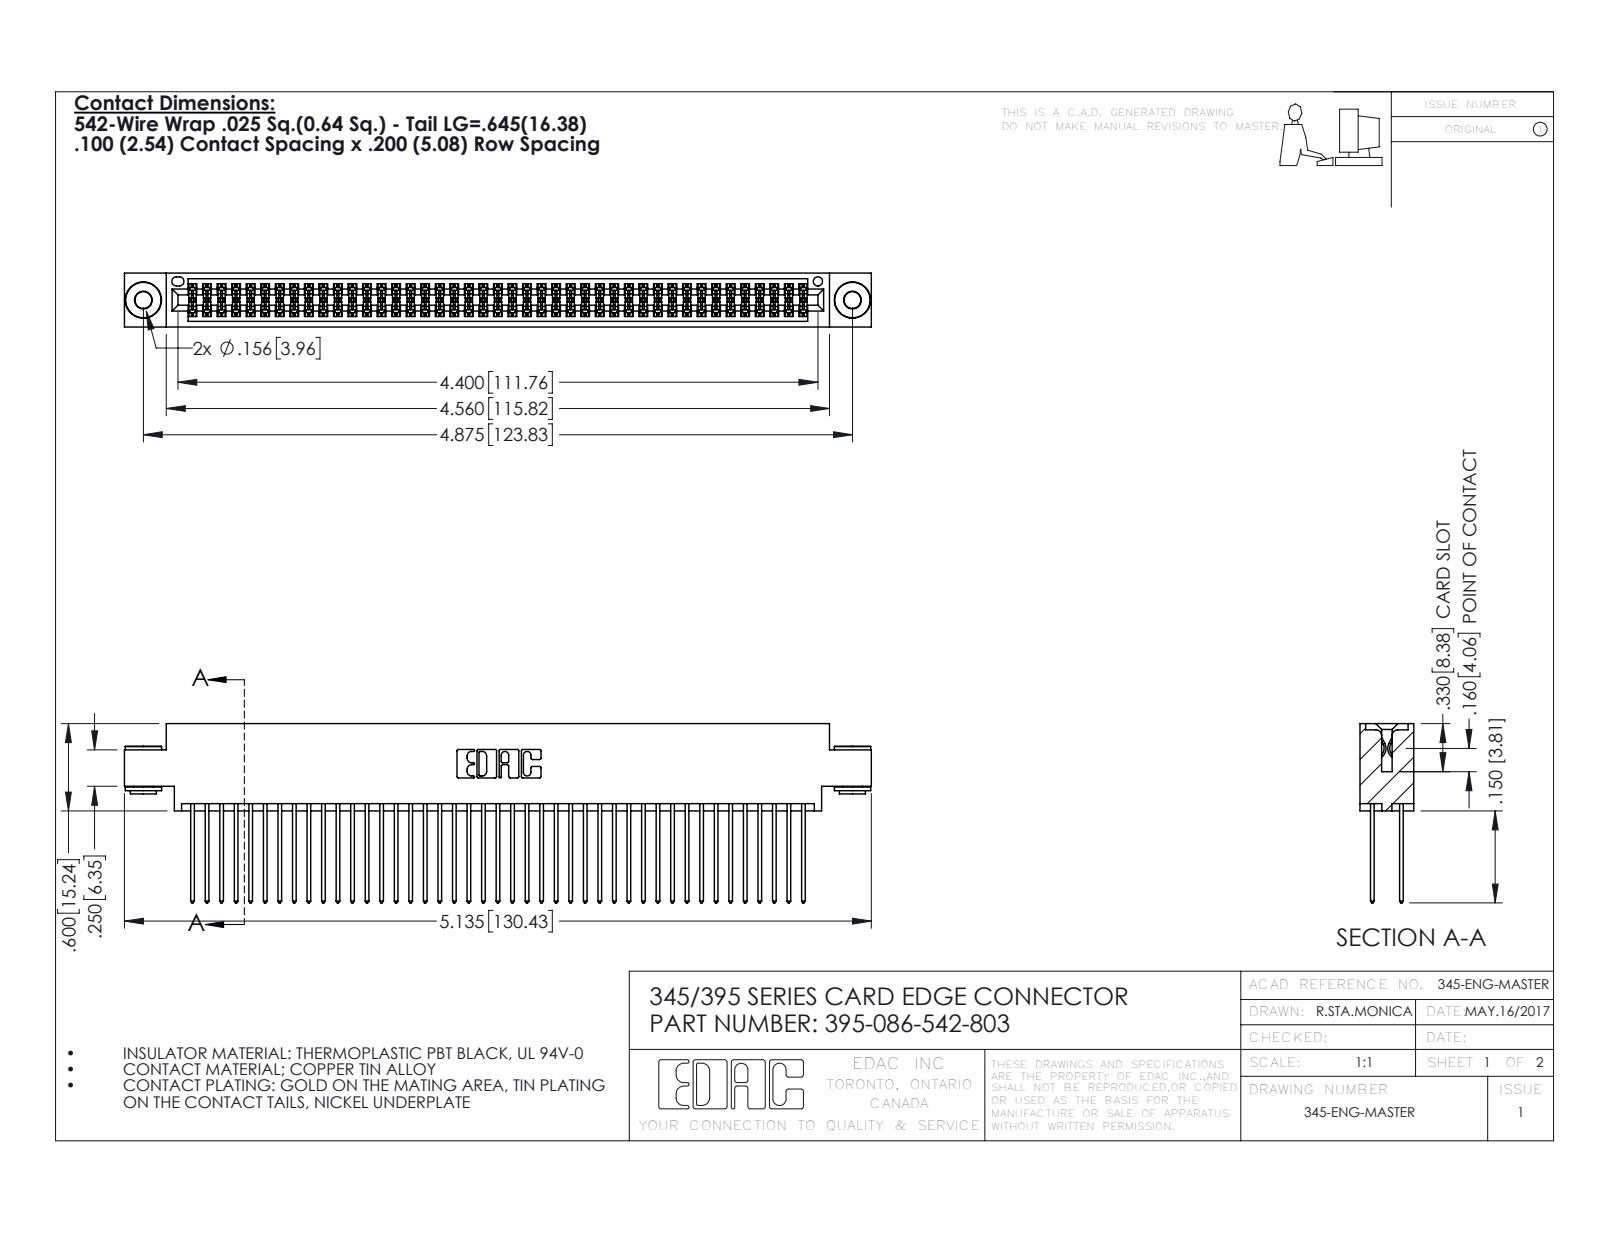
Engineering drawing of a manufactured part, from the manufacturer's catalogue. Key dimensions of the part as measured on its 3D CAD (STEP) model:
Part name (STEP PRODUCT): 345-250-002_345-250-002-102; 395-086-542-803; 345-292-001_345-293-142; 345 Part_0.170 Offset - 0.156 Dia-TH
STEP written by: SolidWorks 2016 (CONFIG_CONTROL_DESIGN)
Units: inches
Bodies: 89 solids, 4468 faces (2932 planar, 1528 cylindrical, 8 other)
Overall size (bounding box): 5.135 × 1.232 × 0.37
Volume: 0.792 in³ · Surface area: 33.23 in²
Round holes (diameter × count): ⌀0.116 ×2, ⌀0.156 ×2, ⌀0.064 ×1
Round bosses / shafts (diameter × count): ⌀0.25 ×2, ⌀0.18 ×2, ⌀0.136 ×2
Partial cylindrical surfaces — rounded edges, fillets, slot ends (radius × count): R0.006 ×129, R0.01 ×86, R0.01 ×22, R0.007 ×6, R0.031 ×6, R0.026 ×3, R0.014 ×2, R0.019 ×2
Main face-to-face distances: 0.072, 0.298, 0.2, 0.098, 0.272, 0.025, 0.37, 0.225, 0.175, 0.149
Hole centre spacings: 0.27, 4.639, 4.875
